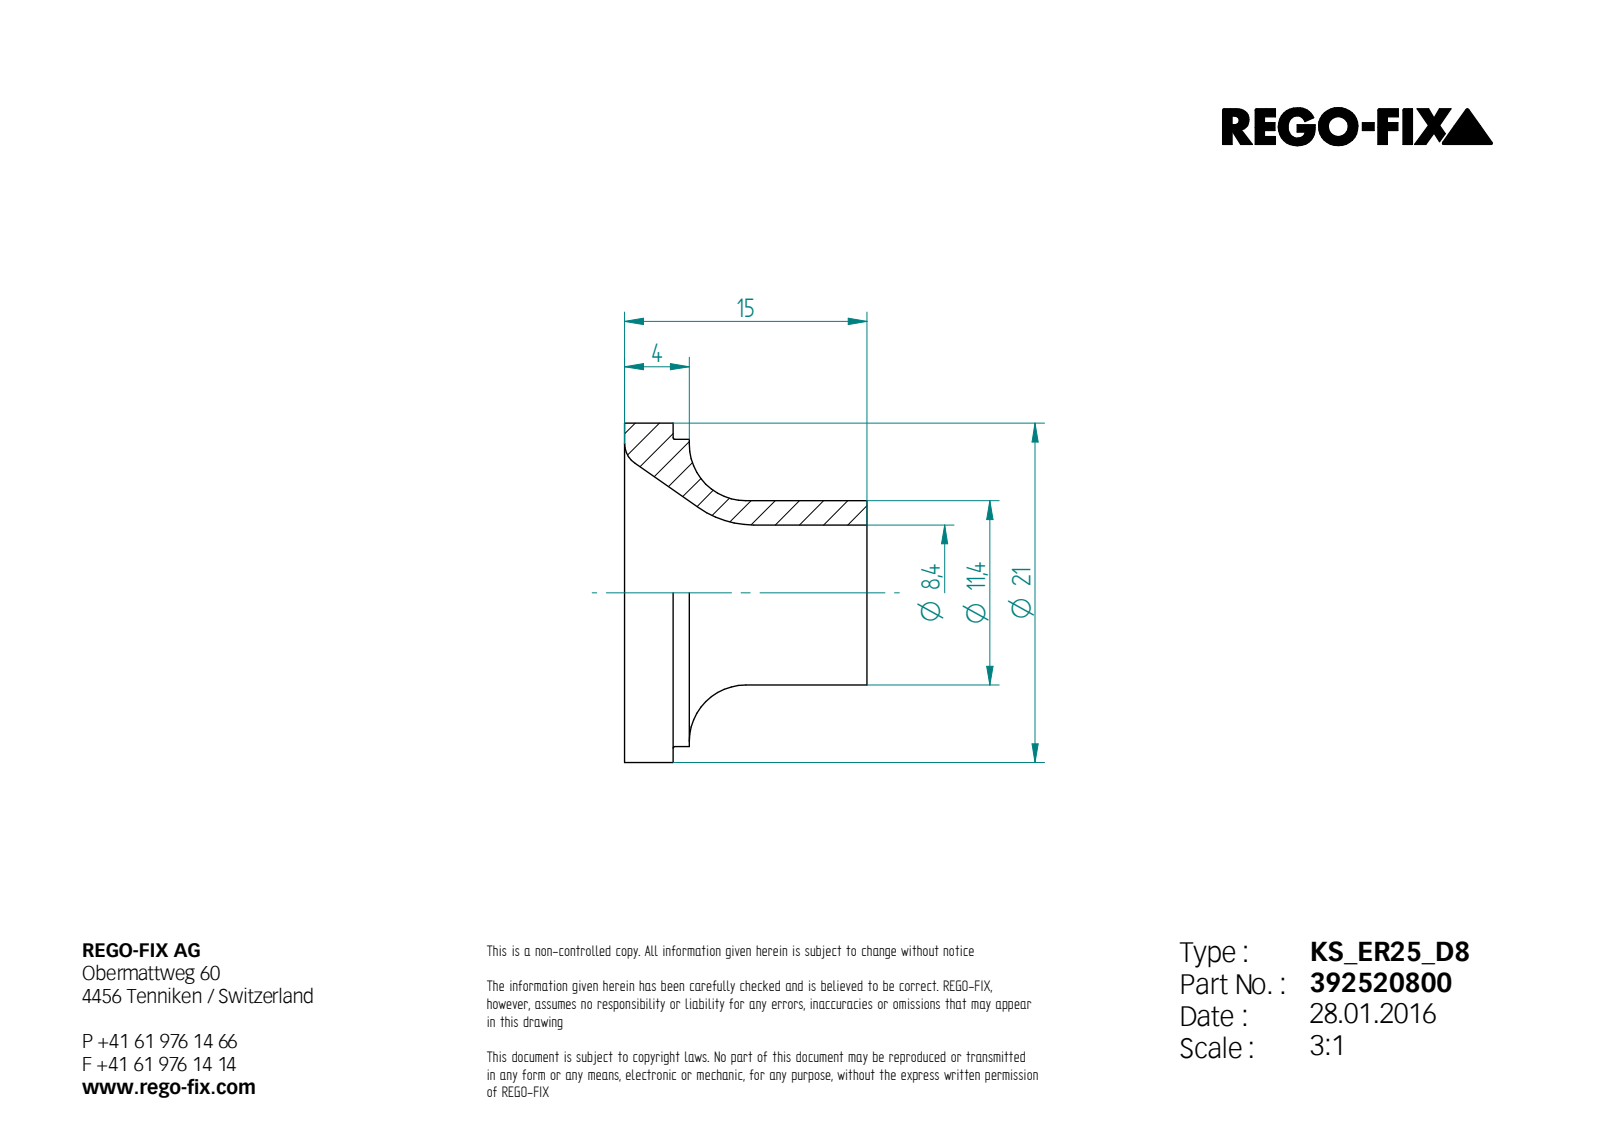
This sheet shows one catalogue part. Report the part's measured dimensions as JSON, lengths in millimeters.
{"step_written_by": "Unknown (AUTOMOTIVE_DESIGN)", "units": "millimeters", "bodies": {"solids": 1, "faces": 13, "planar": 4, "cylindrical": 4, "other": 5}, "overall_size": [21, 21, 15], "volume_mm3": 1246, "surface_area_mm2": 1536, "round_holes": [[8.4, 1]], "round_bosses_or_shafts": [[21, 1], [19, 1], [11.4, 1]], "face_to_face_distances": [3, 15, 12, 4, 1, 11]}
